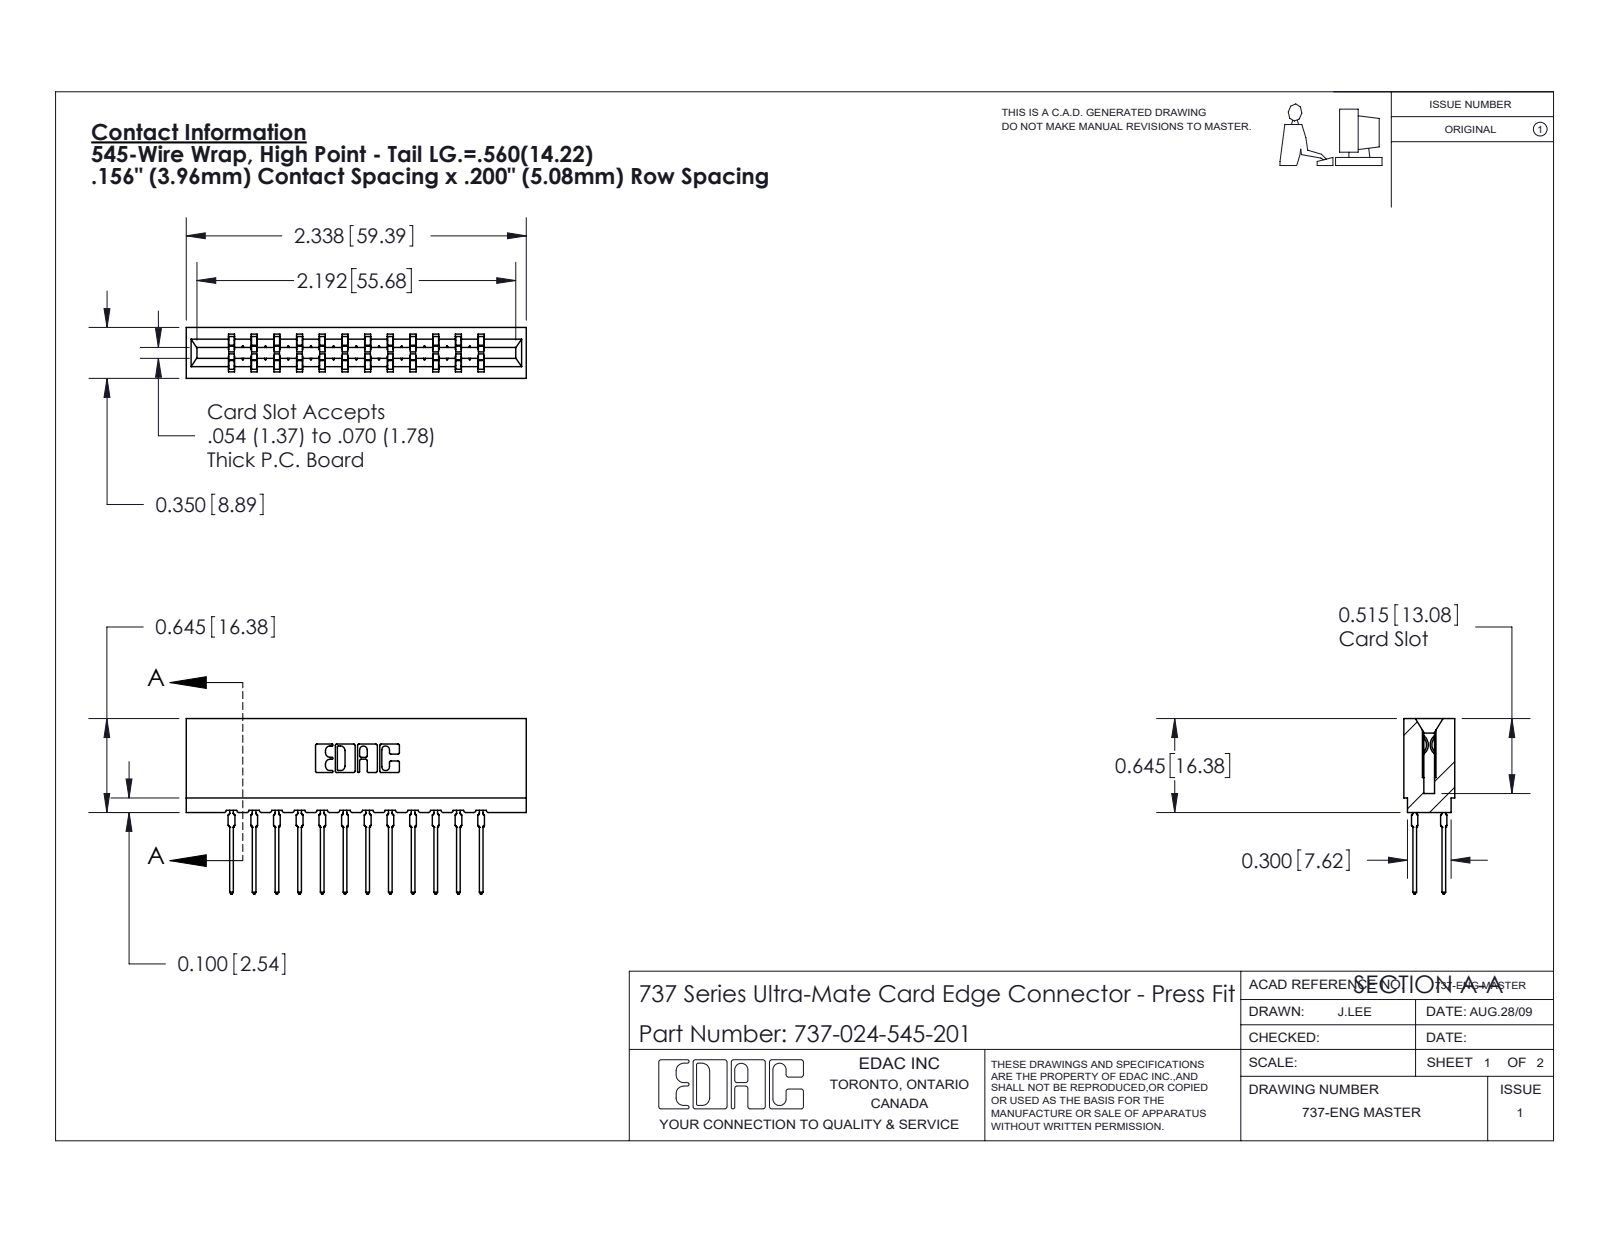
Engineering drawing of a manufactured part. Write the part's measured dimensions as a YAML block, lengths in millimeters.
part_name: "737-024-545-201; 737 Part_Insulator Option - 01; 745-292-001_545"
step_written_by: "SolidWorks 2020 (CONFIG_CONTROL_DESIGN)"
units: millimeters
bodies: {solids: 25, faces: 2254, planar: 1170, cylindrical: 460, other: 624}
overall_size: [59.4, 30.6, 8.9]
volume: 6150
surface_area: 8671
partial_cylinders:
  - {radius: 0.5, count: 48}
  - {radius: 0.4, count: 24}
  - {radius: 0.3, count: 22}
  - {radius: 0.1, count: 8}
  - {radius: 0.3, count: 8}
  - {radius: 0.2, count: 6}
  - {radius: 0.8, count: 6}
  - {radius: 0.7, count: 3}
face_to_face_distances: [3.5, 5.4, 4, 8.9, 15.8, 1.6, 7.3, 1.9, 3.8, 7.9]
